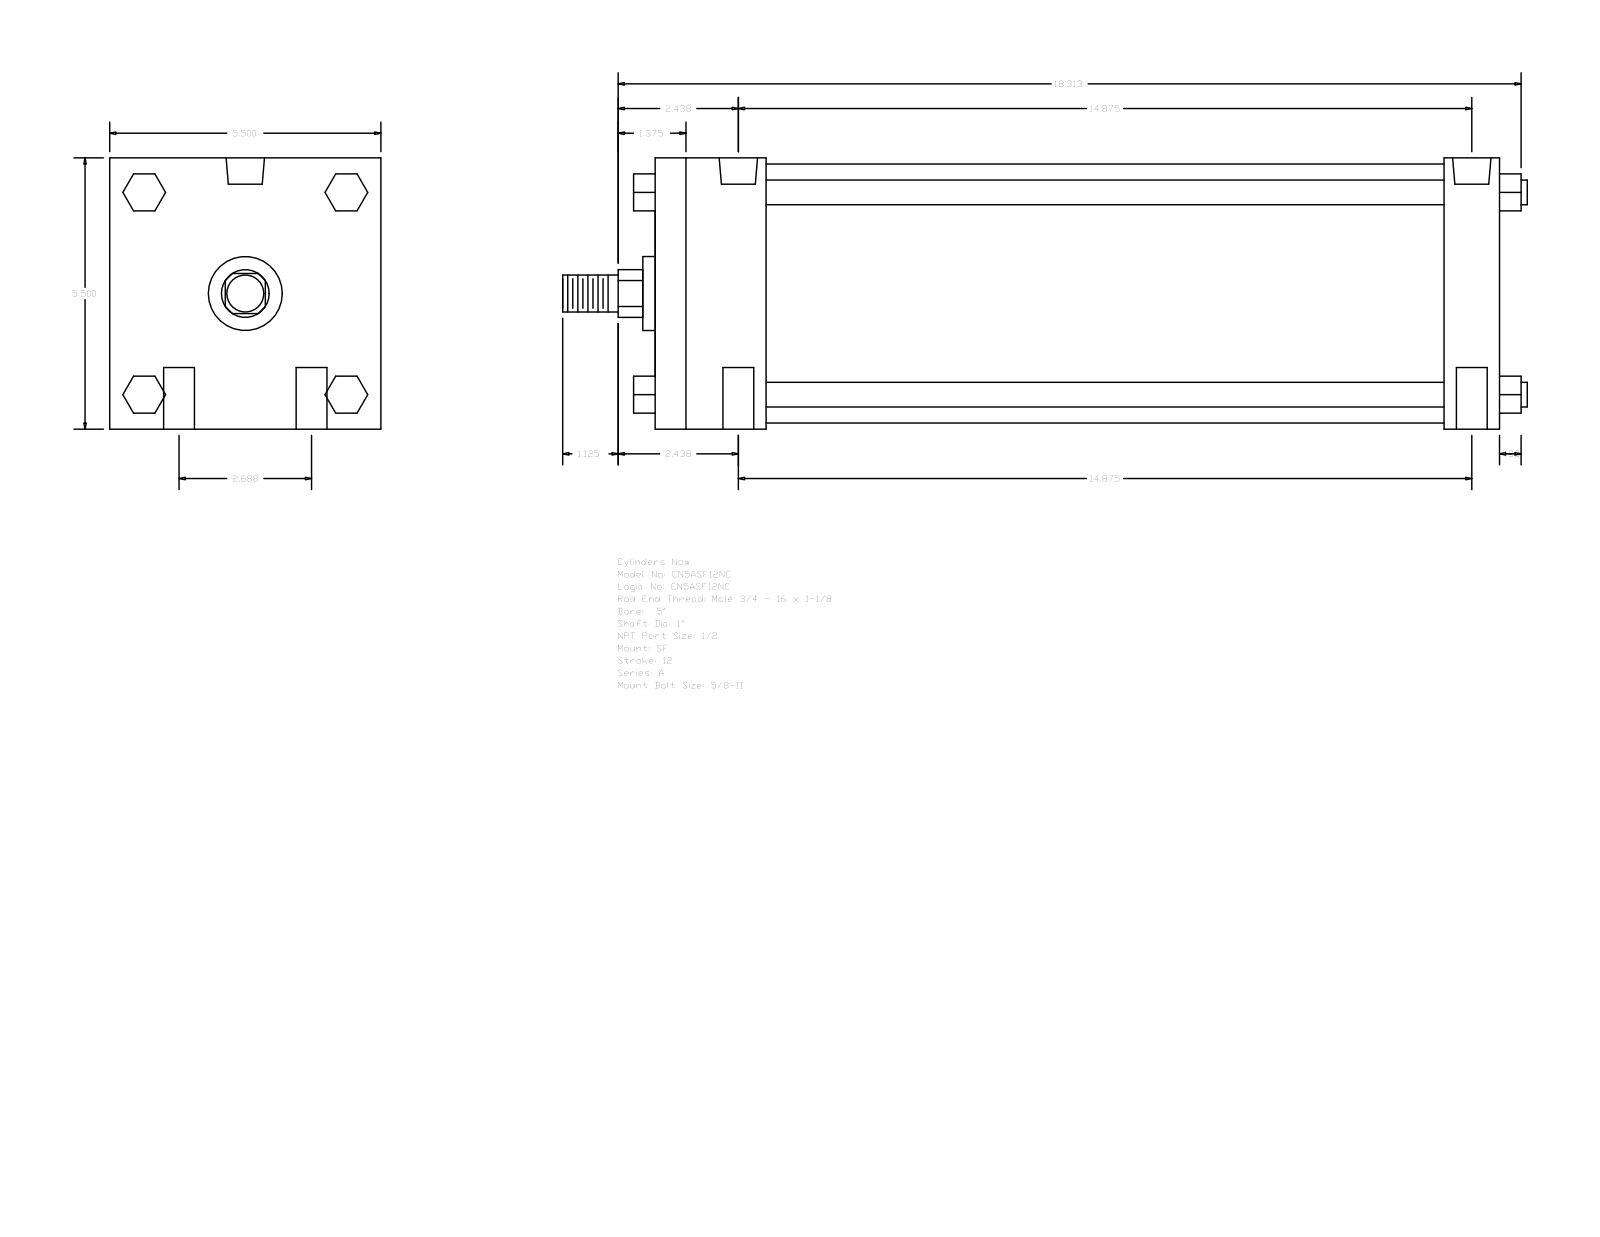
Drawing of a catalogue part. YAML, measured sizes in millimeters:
part_name: "A_SF__0500_1"
step_written_by: "GSSL Pune (CONFIG_CONTROL_DESIGN)"
units: millimeters
bodies: {solids: 0, faces: 124, planar: 94, cylindrical: 30, other: 0}
overall_size: [496.89, 139.7, 139.7]
round_holes:
  - {diameter: 15.88, count: 4}
  - {diameter: 8.73, count: 2}
  - {diameter: 19.77, count: 2}
round_bosses_or_shafts:
  - {diameter: 12.7, count: 4}
  - {diameter: 133.35, count: 1}
  - {diameter: 38.1, count: 1}
  - {diameter: 25.4, count: 1}
  - {diameter: 19.05, count: 1}
partial_cylinders:
  - {radius: 12.29, count: 1}
face_to_face_distances: [139.7, 434.97, 28.57, 57.15, 406.4, 349.25, 377.82, 19.05, 52.07, 90.18]
hole_center_spacings: [34.13, 379.37, 377.83, 68.26, 383.95, 373.05]
